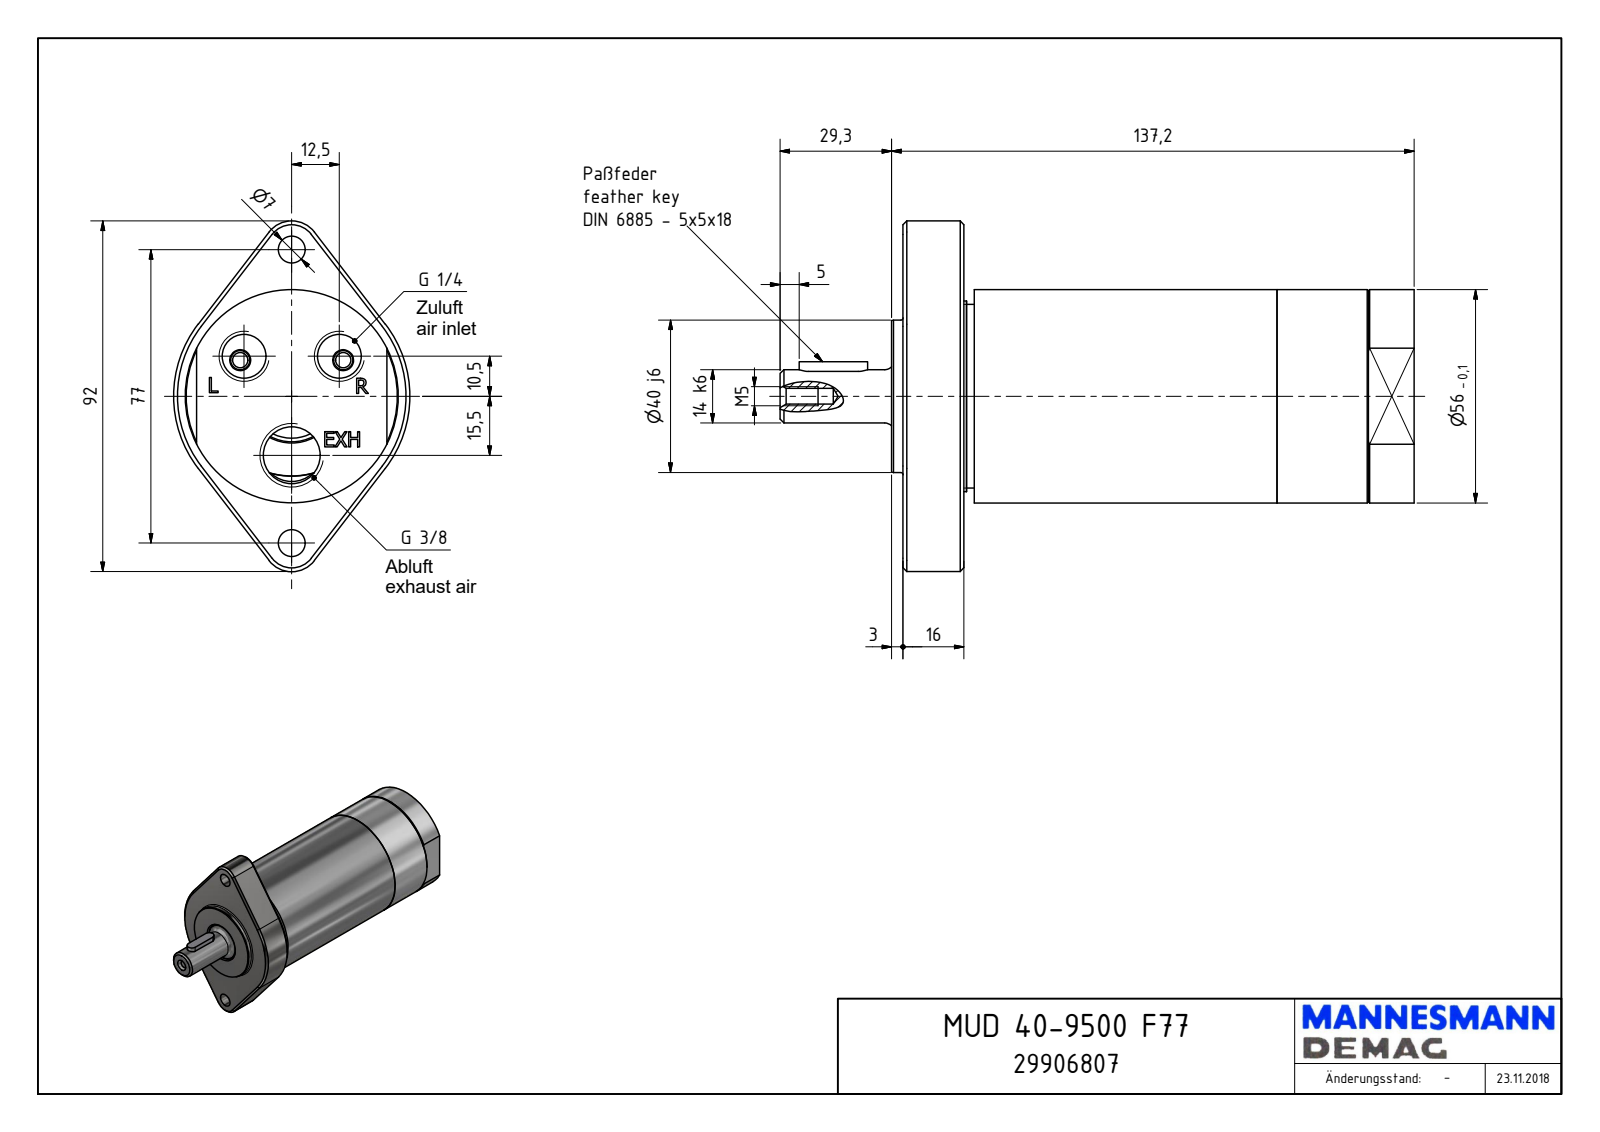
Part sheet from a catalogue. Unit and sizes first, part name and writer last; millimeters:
Units: millimetres
Overall size (bounding box): 166.5 × 92 × 62
Round holes (diameter × count): ⌀7 ×2, ⌀11.45 ×2, ⌀4.13 ×1, ⌀14.95 ×1, ⌀21 ×1, ⌀21.25 ×1, ⌀23.54 ×1, ⌀26 ×1, ⌀48.38 ×1
Round bosses / shafts (diameter × count): ⌀56 ×1, ⌀50 ×1, ⌀48.18 ×1, ⌀40 ×1, ⌀19.85 ×1, ⌀14 ×1
Partial cylindrical surfaces — rounded edges, fillets, slot ends (radius × count): R2.5 ×2, R6 ×2, R7.5 ×2, R19.32 ×1, R23 ×1, R31 ×1
Main face-to-face distances: 134.2, 16, 118.2, 19, 3, 137.2, 21.7, 18.7, 2.7, 115.5
Hole centre spacings: 16.32, 28.85, 30.66, 38.5, 50.57, 15.5, 23, 25
Volume: 349 466 mm³ · Surface area: 39 831 mm²
Bodies: 1 solid, 186 faces (105 planar, 35 cylindrical, 46 other)
Part name (STEP PRODUCT): MUD 40-9500 F77_29906807
STEP written by: Autodesk Inventor 2018 (AUTOMOTIVE_DESIGN)
